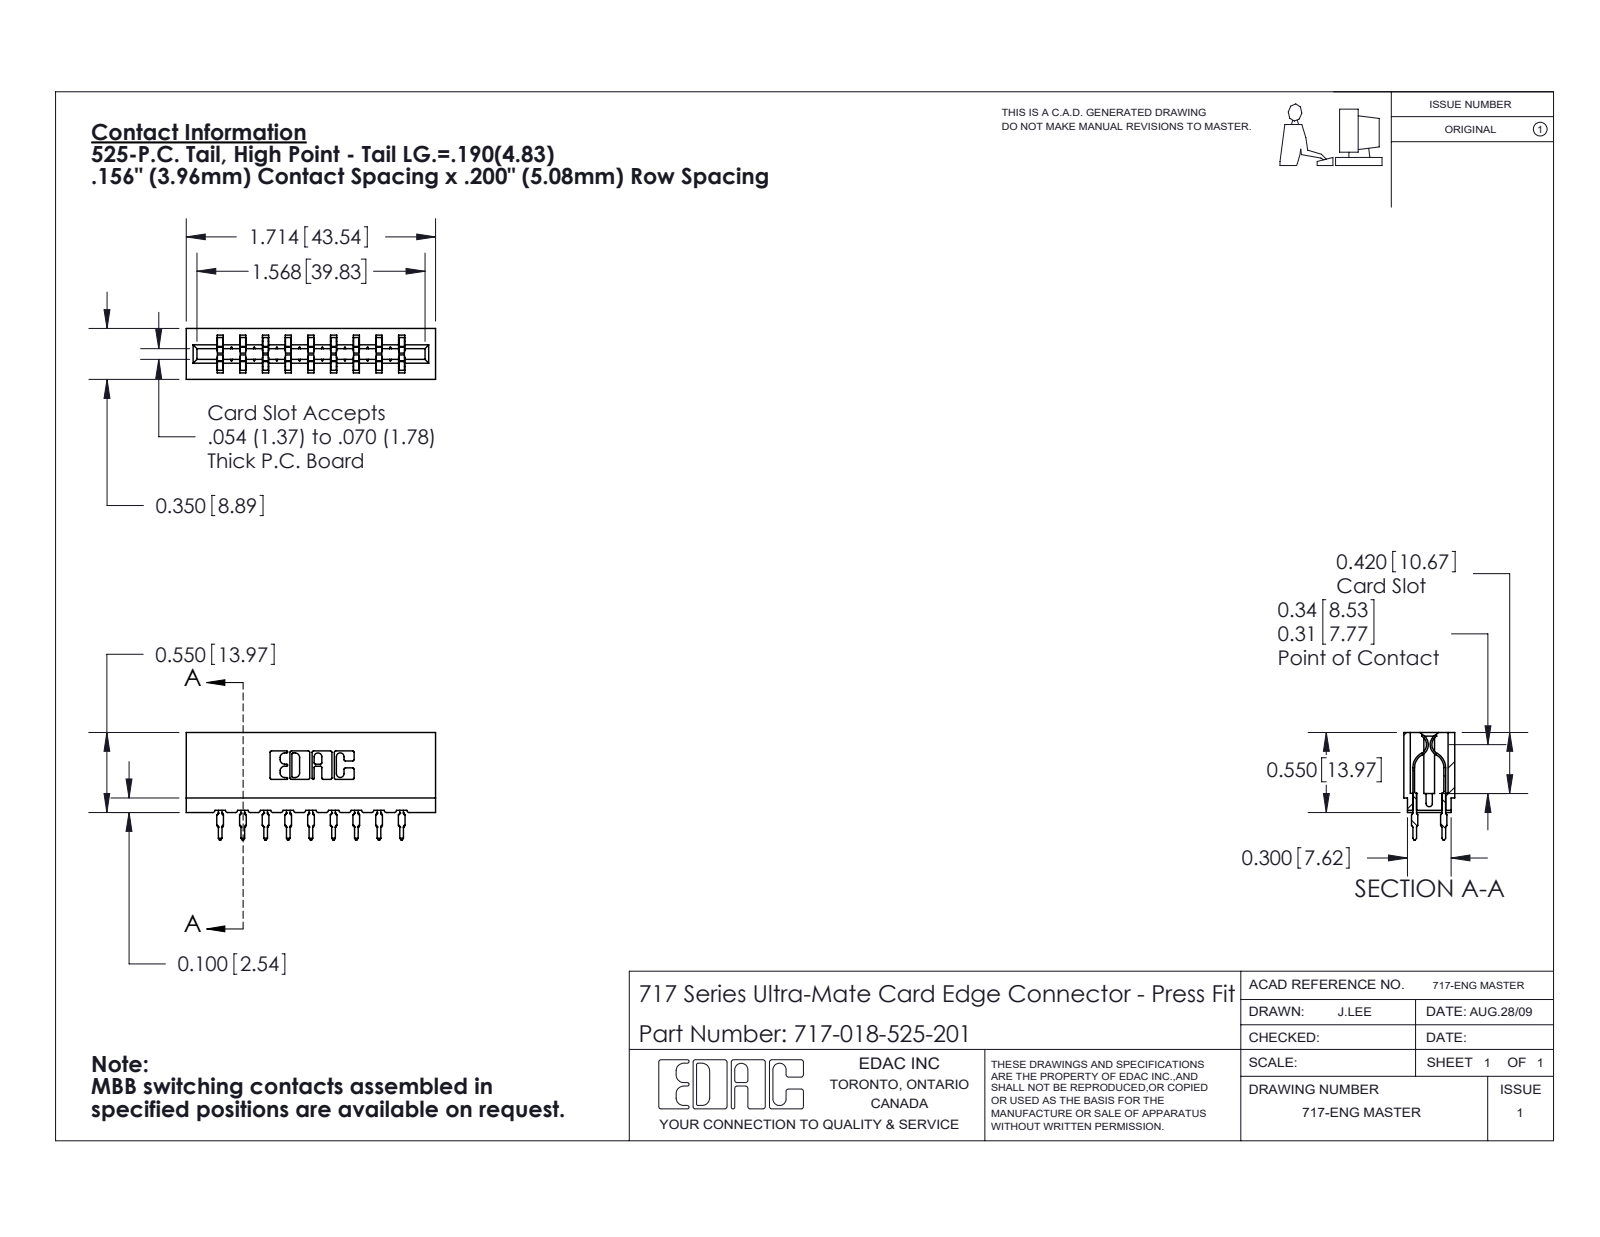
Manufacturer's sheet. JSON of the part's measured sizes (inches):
{"part_name": "745-292-001_525; 717-018-525-201; 717 Part_Insulator Option - 06", "step_written_by": "SolidWorks 2020 (CONFIG_CONTROL_DESIGN)", "units": "inches", "bodies": {"solids": 19, "faces": 1714, "planar": 891, "cylindrical": 355, "other": 468}, "overall_size": [1.714, 0.739, 0.35], "volume_in3": 0.238, "surface_area_in2": 8.539, "partial_cylinders_radius": [[0.021, 36], [0.01, 22], [0.015, 18], [0.005, 8], [0.011, 8], [0.007, 6], [0.031, 6], [0.026, 3]], "face_to_face_distances": [0.156, 0.212, 0.624, 0.138, 0.468, 0.198, 0.35, 0.312, 0.042, 0.312]}
